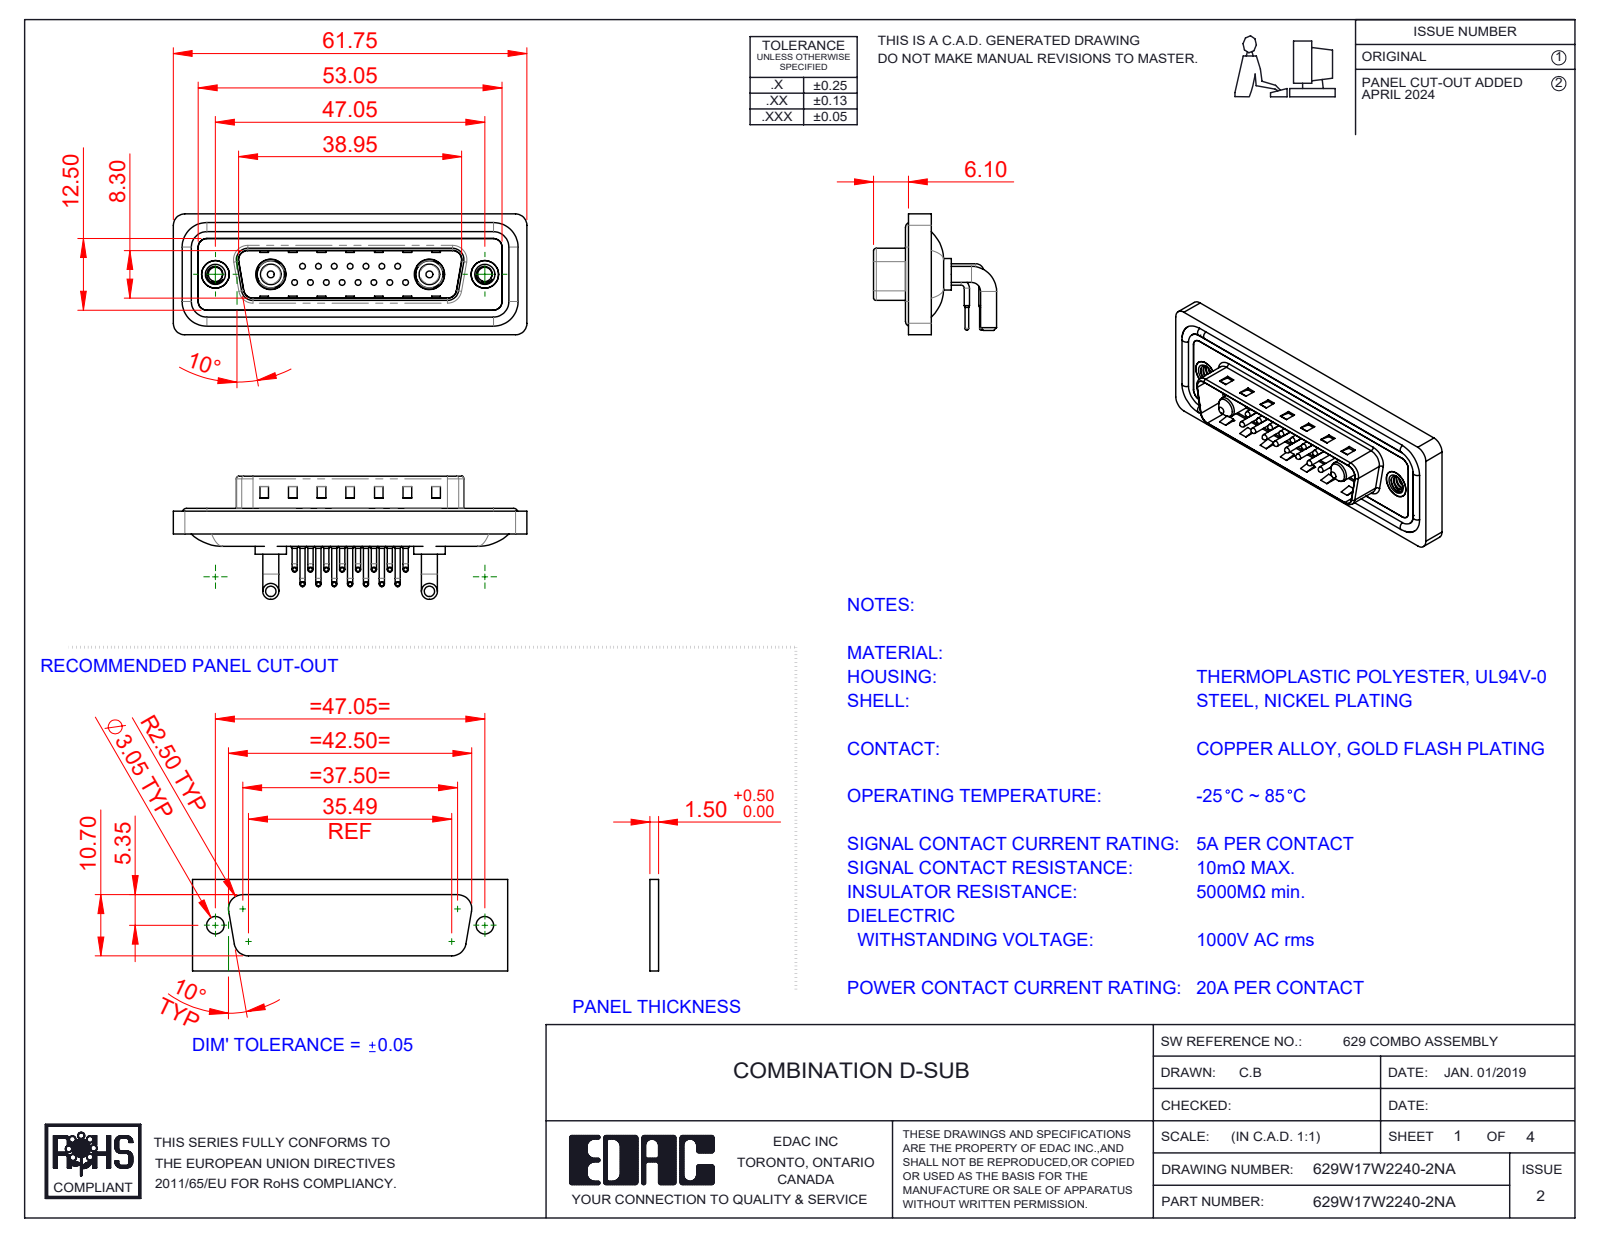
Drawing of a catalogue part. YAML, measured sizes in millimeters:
part_name: "629Combo Shell Rear_25 Contacts; 629Combo Threaded Rivet_A; 629W17W2140-2NA; Power Pin_20A RA (+5 more)"
step_written_by: "SolidWorks 2023 (CONFIG_CONTROL_DESIGN)"
units: millimeters
bodies: {solids: 26, faces: 2213, planar: 1189, cylindrical: 768, other: 256}
overall_size: [61.75, 21.5, 21.1]
volume: 7516
surface_area: 12605
round_holes:
  - {diameter: 0.75, count: 15}
  - {diameter: 1.6, count: 15}
  - {diameter: 2, count: 15}
  - {diameter: 2.5, count: 2}
  - {diameter: 4, count: 2}
  - {diameter: 4.8, count: 2}
  - {diameter: 4.85, count: 2}
  - {diameter: 5, count: 2}
  - {diameter: 5.3, count: 2}
round_bosses_or_shafts:
  - {diameter: 0.9, count: 30}
  - {diameter: 1.5, count: 15}
  - {diameter: 1, count: 15}
  - {diameter: 0.65, count: 15}
  - {diameter: 2.8, count: 4}
  - {diameter: 1.6, count: 4}
  - {diameter: 5.5, count: 2}
  - {diameter: 5.2, count: 2}
partial_cylinders:
  - {radius: 1.5, count: 18}
  - {radius: 2, count: 18}
  - {radius: 1.01, count: 15}
  - {radius: 0.5, count: 8}
  - {radius: 1.6, count: 8}
  - {radius: 0.25, count: 4}
  - {radius: 0.6, count: 4}
  - {radius: 0.65, count: 4}
face_to_face_distances: [0.4, 2.9, 0.8, 4.1, 1.1, 2.1, 1.6, 4.5, 1.5, 2.5]
hole_center_spacings: [3.16, 2.77, 5.54, 8.31, 5.04, 7.49, 11.08, 5.03]
